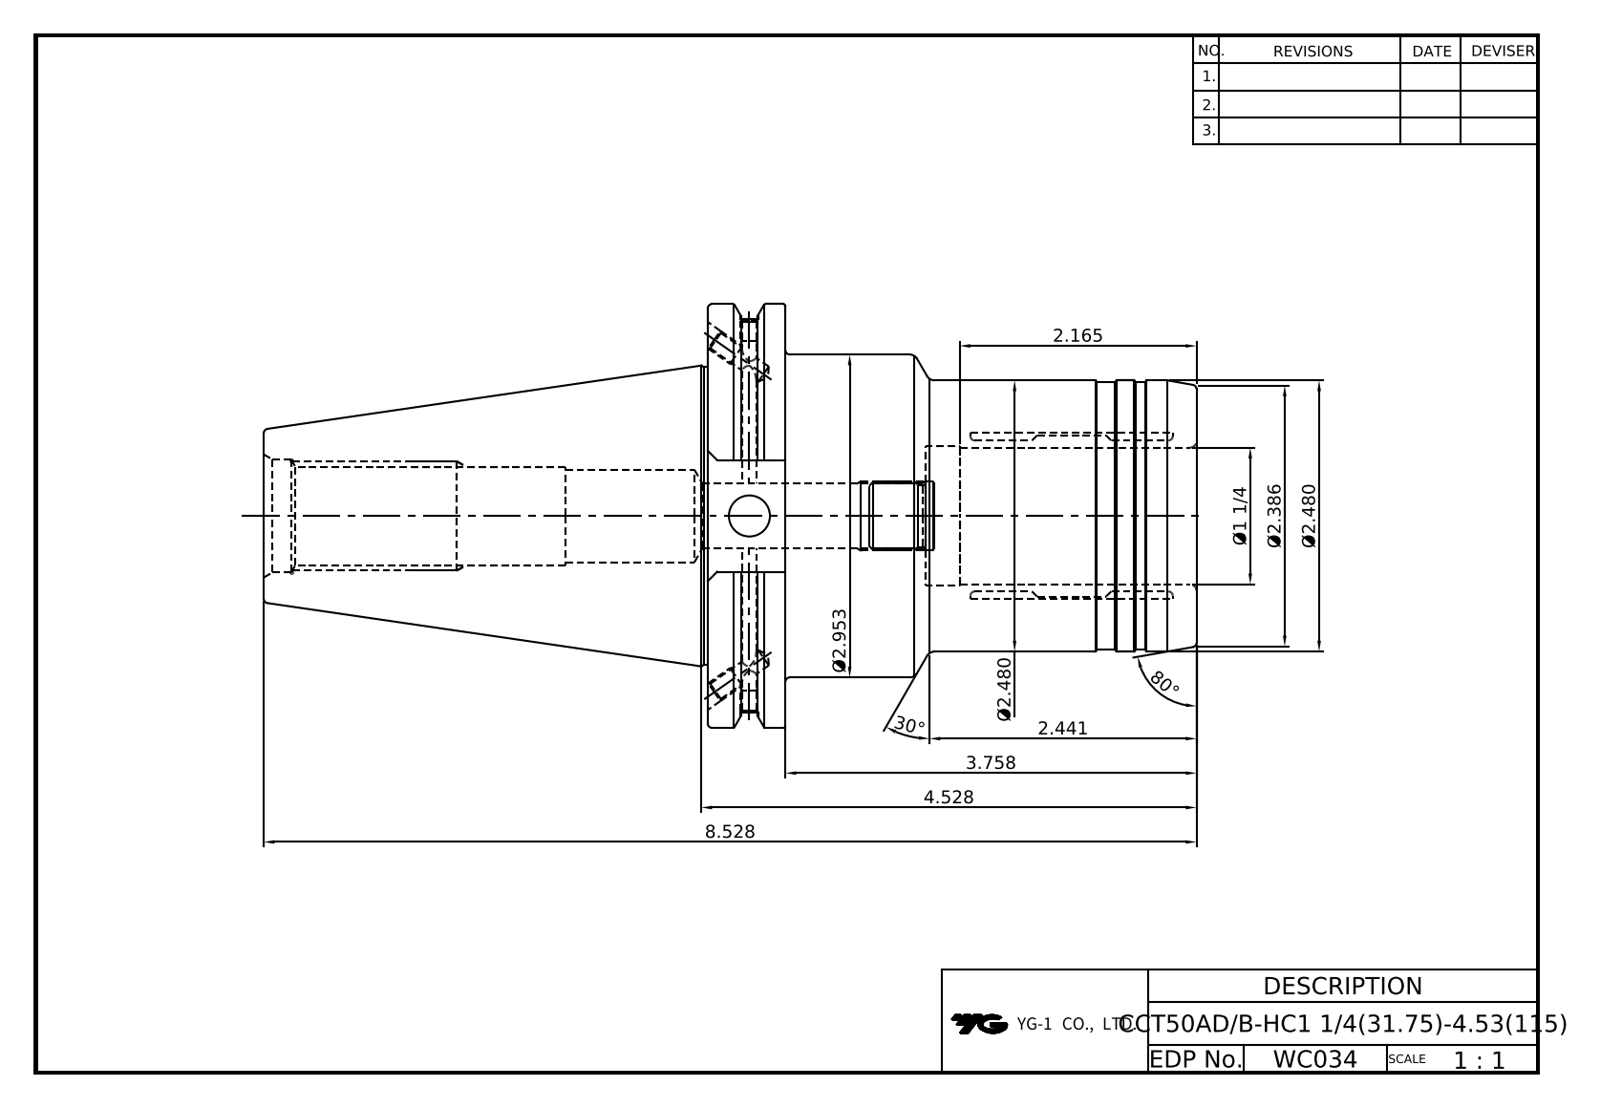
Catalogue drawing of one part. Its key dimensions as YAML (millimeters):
part_name: "LO-CCT50ADB-HC31.75-105"
step_written_by: "Autodesk Inventor 2022 (AUTOMOTIVE_DESIGN)"
units: millimeters
bodies: {solids: 1, faces: 110, planar: 40, cylindrical: 32, other: 38}
overall_size: [216.6, 98.42, 94.69]
volume: 605703
surface_area: 72798
round_holes:
  - {diameter: 3.24, count: 2}
  - {diameter: 4.13, count: 2}
  - {diameter: 4.2, count: 2}
  - {diameter: 5, count: 2}
  - {diameter: 9.53, count: 1}
  - {diameter: 14.92, count: 1}
  - {diameter: 21.5, count: 1}
  - {diameter: 21.97, count: 1}
  - {diameter: 26.2, count: 1}
  - {diameter: 31.75, count: 1}
  - {diameter: 32.6, count: 1}
round_bosses_or_shafts:
  - {diameter: 98.42, count: 1}
  - {diameter: 91.29, count: 1}
  - {diameter: 75, count: 1}
  - {diameter: 69.25, count: 1}
  - {diameter: 63, count: 1}
  - {diameter: 62, count: 1}
face_to_face_distances: [17.55, 113.5, 95.95, 50.5, 32.95, 63, 103.1, 120.65, 153.6, 216.6]
